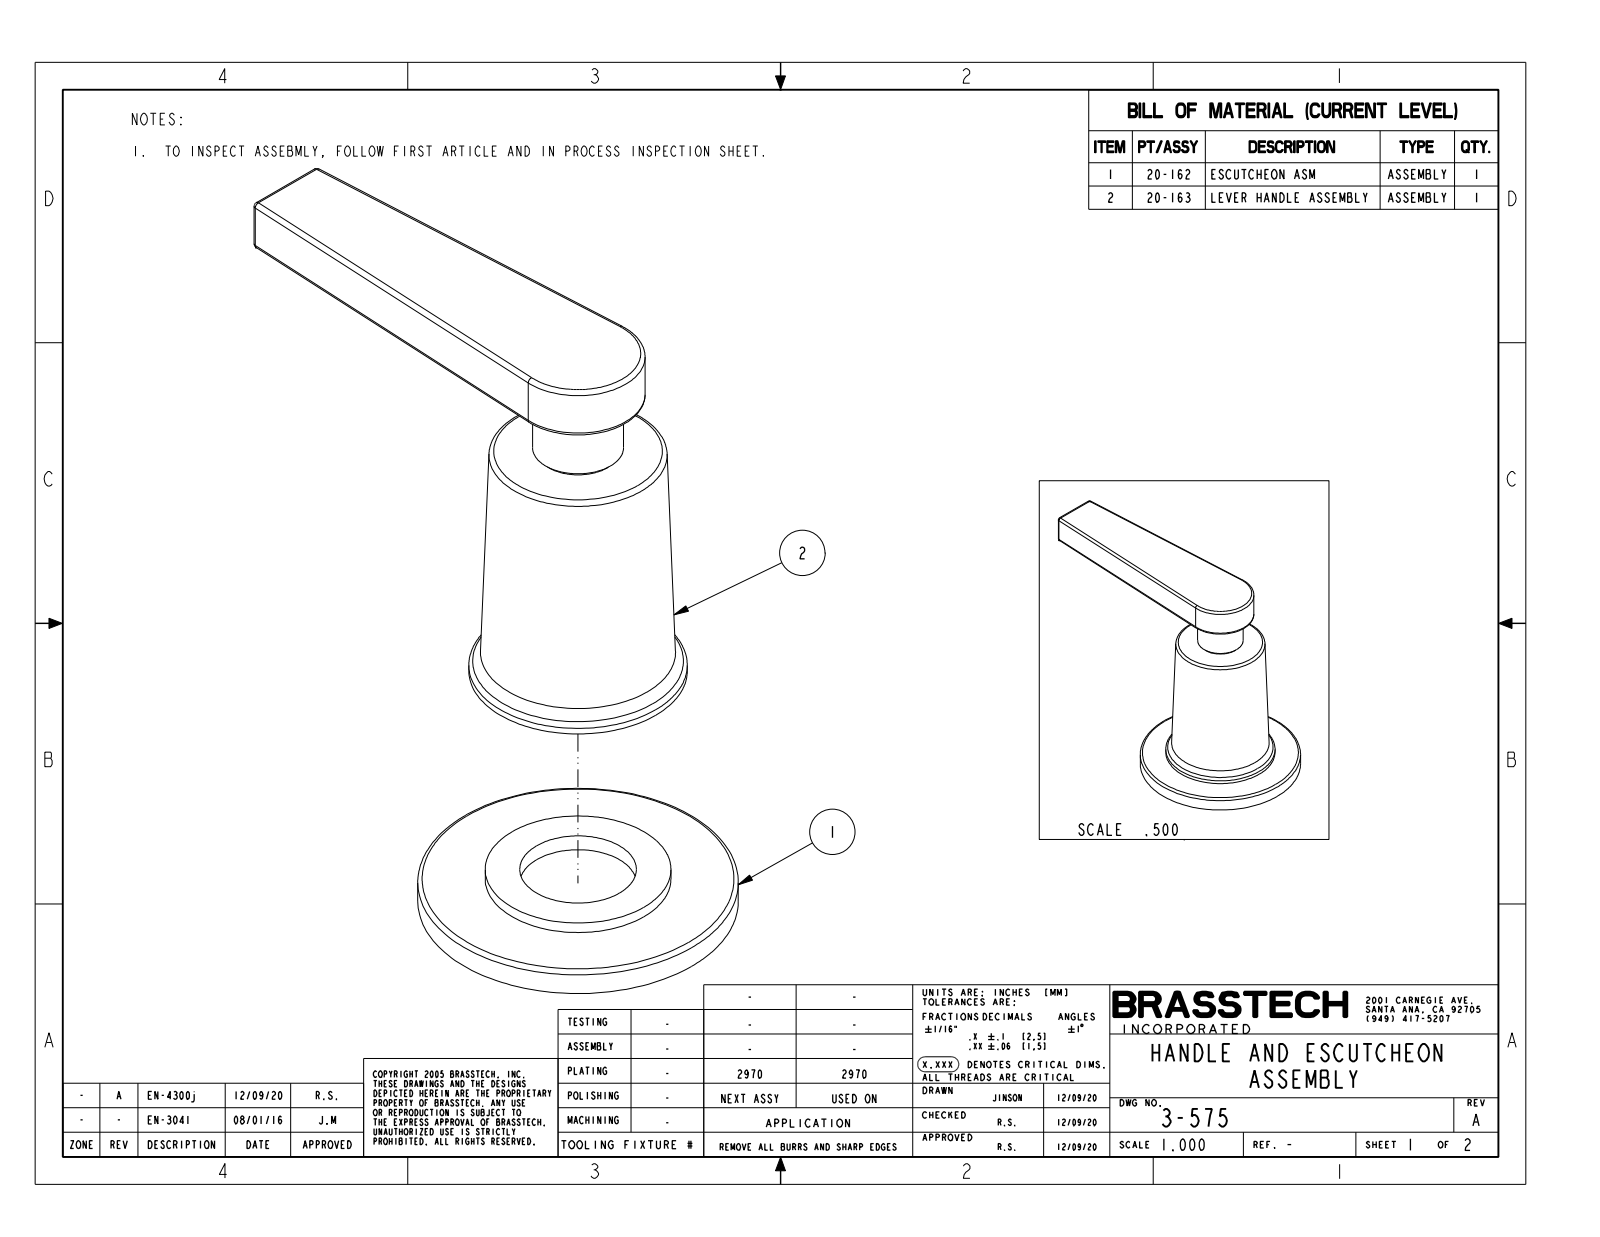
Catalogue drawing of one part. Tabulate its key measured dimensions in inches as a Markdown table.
| quantity | value |
| --- | --- |
| part name | 3-575 |
| STEP written by | CREO PARAMETRIC BY PTC INC, 2018400 (CONFIG_CONTROL_DESIGN) |
| units | inches |
| bodies | 1 solid, 53 faces (12 planar, 23 cylindrical, 18 other) |
| overall size | 3.95 × 2.87 × 2.2 |
| volume | 4.237 in³ |
| surface area | 25.26 in² |
| round holes (diameter × count) | 0.437 × 1 |
| round bosses / shafts (diameter × count) | 2.2 × 1, 1.5 × 1, 1.275 × 1, 0.625 × 1, 0.525 × 1, 0.429 × 1 |
| partial cylindrical surfaces (radius × count) | 0.03 × 8, 0.46 × 1 |
| main face-to-face distances | 0.187, 2.87, 2.683, 2.495, 2.308, 0.375, 2.047, 1.86, 0.448, 0.823 |
